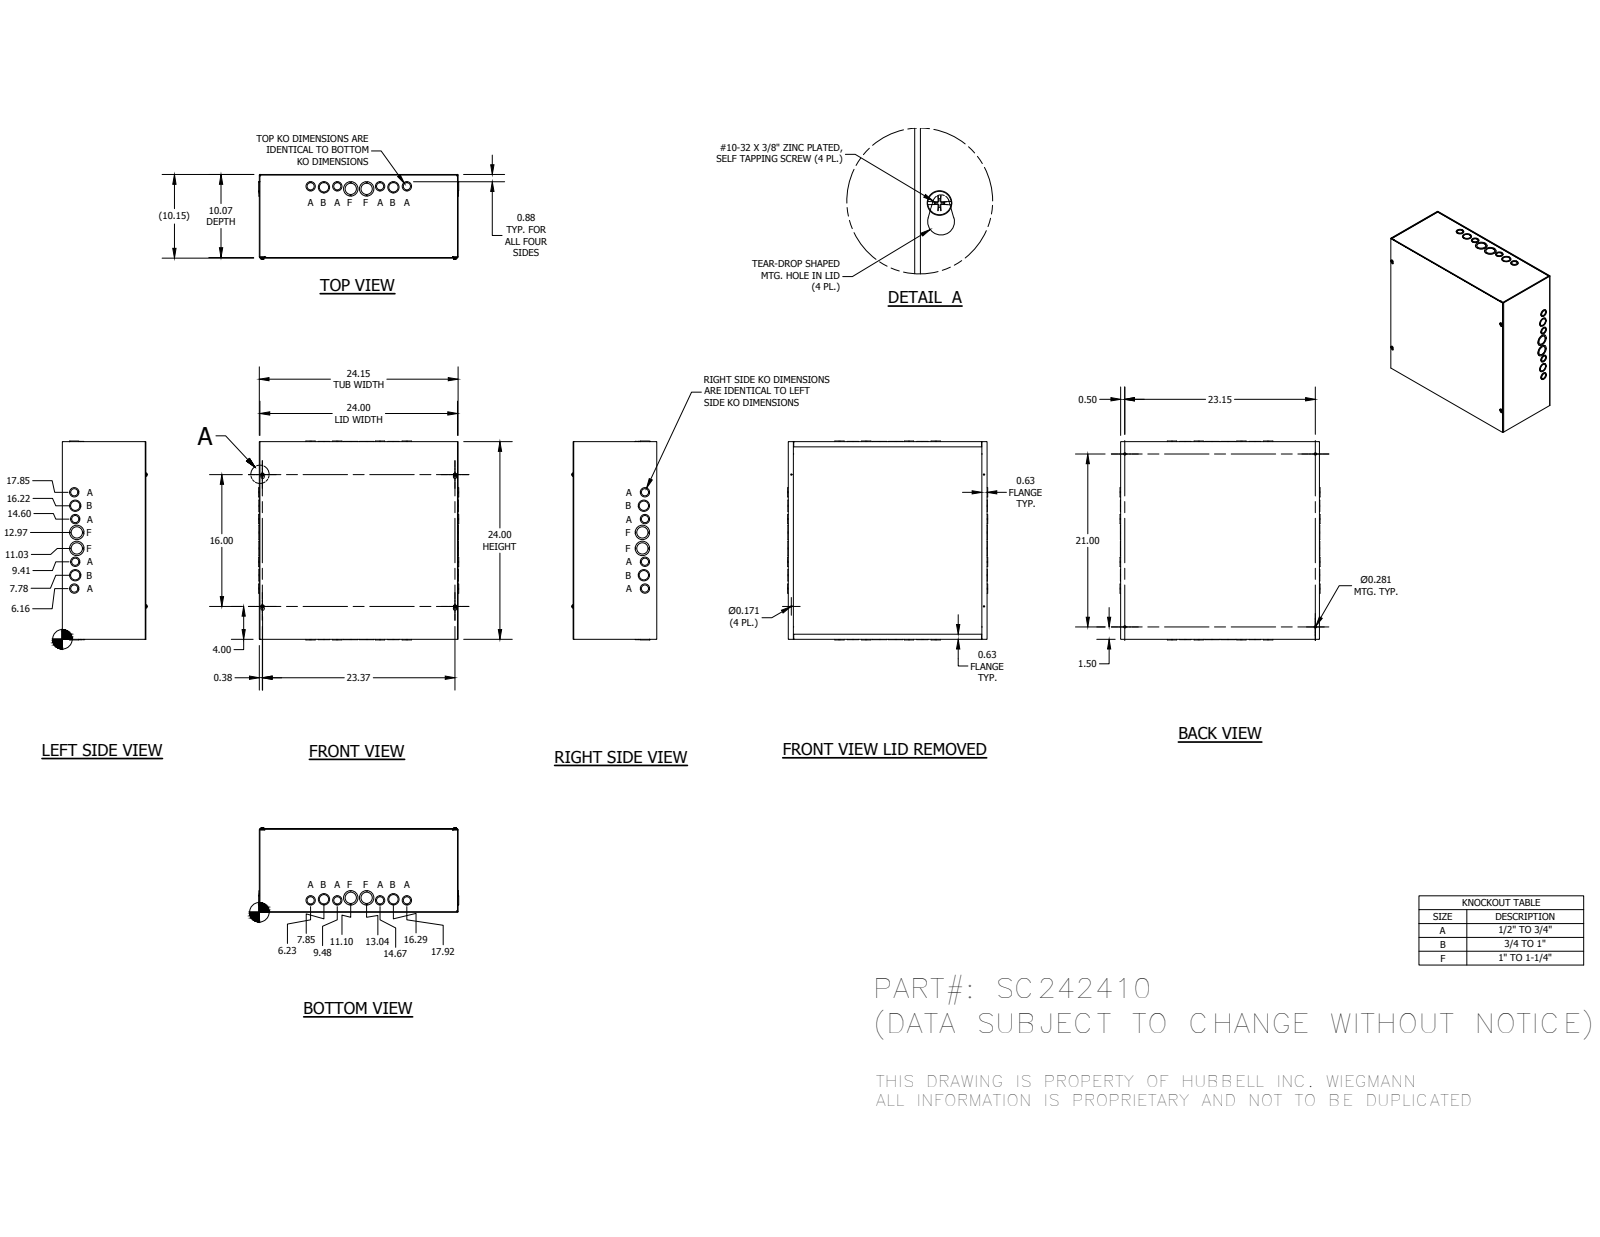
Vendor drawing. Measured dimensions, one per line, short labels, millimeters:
name: SC242412BLR; SC2412TB; SC2424LPA; 37214 (+1 more)
written by: Autodesk Inventor 2014 (AUTOMOTIVE_DESIGN)
unit: mm
bodies: 37 solids, 1219 faces (899 planar, 236 cylindrical, 84 other)
size: 617.12 × 613.36 × 311.91
holes: 14× ⌀28.57, 10× ⌀22.22, 8× ⌀34.92, 4× ⌀4.34, 4× ⌀7.14, 4× ⌀44.45
bosses: 4× ⌀4.83
rounds: 12× R0.4, 12× R2.28, 4× R3.17, 4× R5.16
face distances: 1.88, 306.68, 304.8, 609.6, 607.72, 611.48, 308.56, 613.36, 605.84, 3.76
hole spacings: 41.39, 41.4, 42.03, 63.58, 82.55, 82.69, 90.9, 124.07
